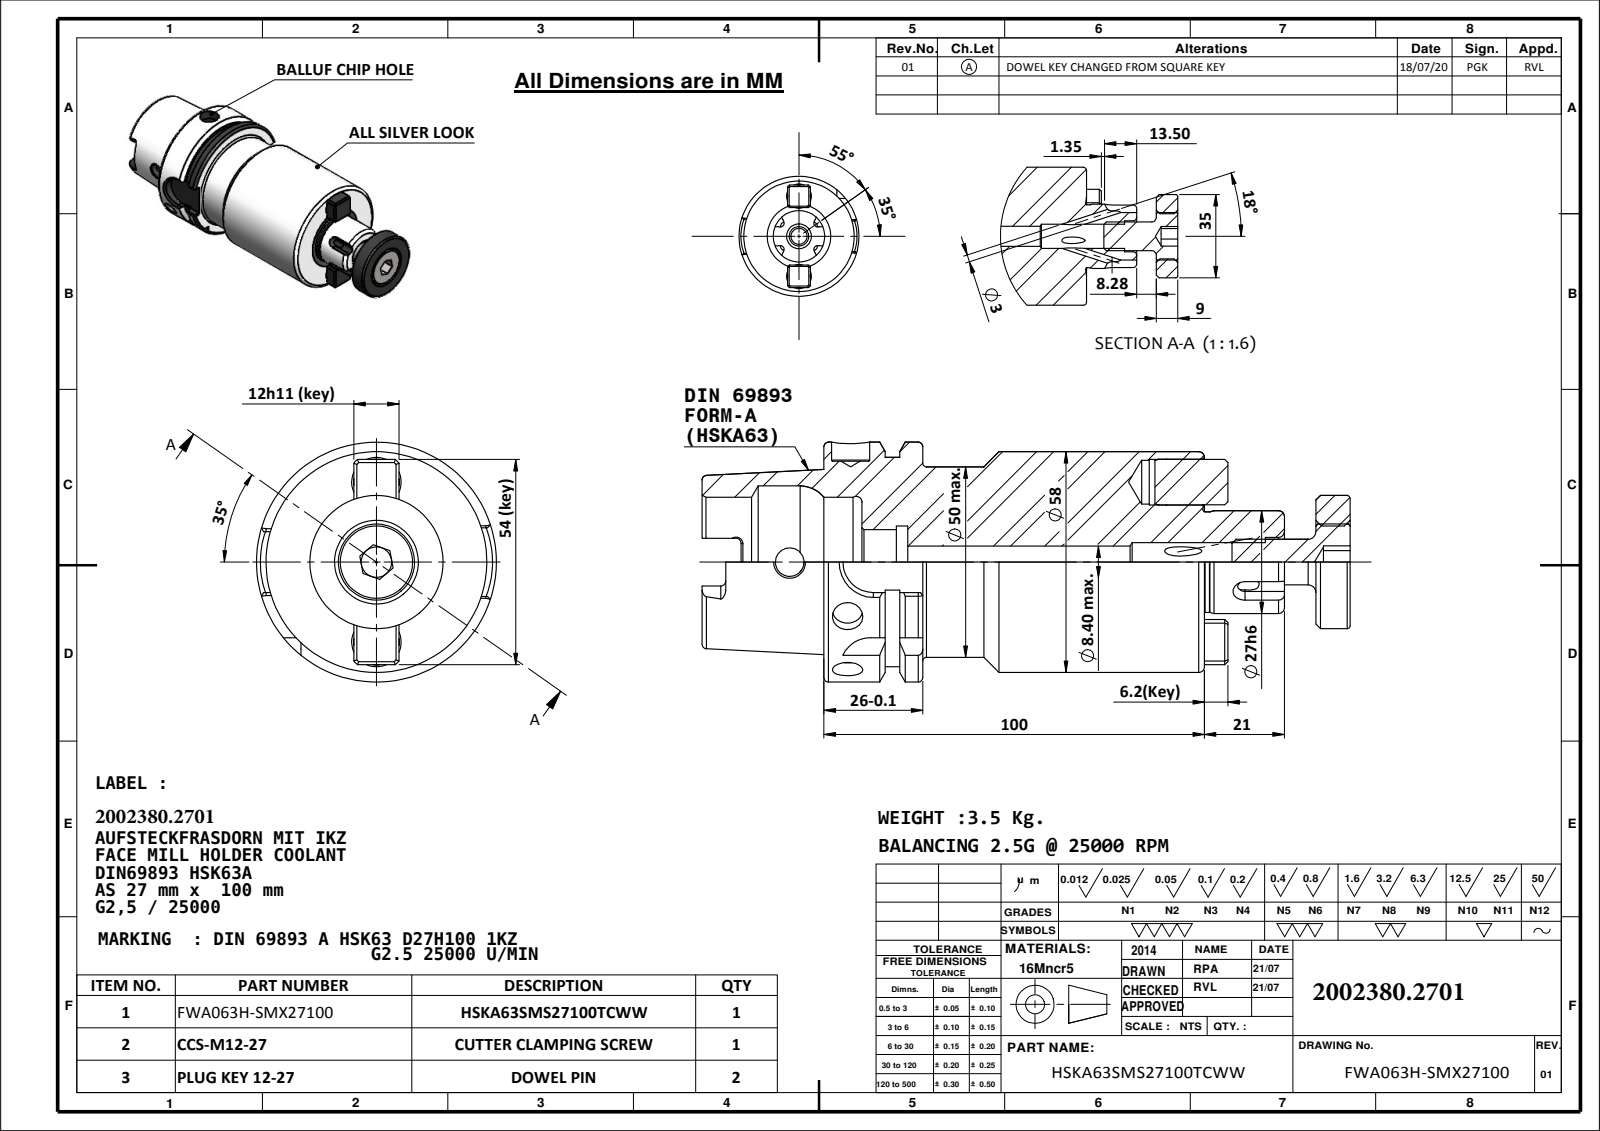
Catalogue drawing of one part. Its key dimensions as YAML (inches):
part_name: "9163A-AS527100; PLUG KEY 12-27.IGS; CCS-M12-27-2.IGS; CCS-M12-27-1.IGS (+1 more)"
step_written_by: "SolidWorks 2018 (AUTOMOTIVE_DESIGN)"
units: inches
bodies: {solids: 5, faces: 355, planar: 0, cylindrical: 0, other: 355}
overall_size: [6.702, 2.48, 2.48]
volume: 17.06
surface_area: 76.58
